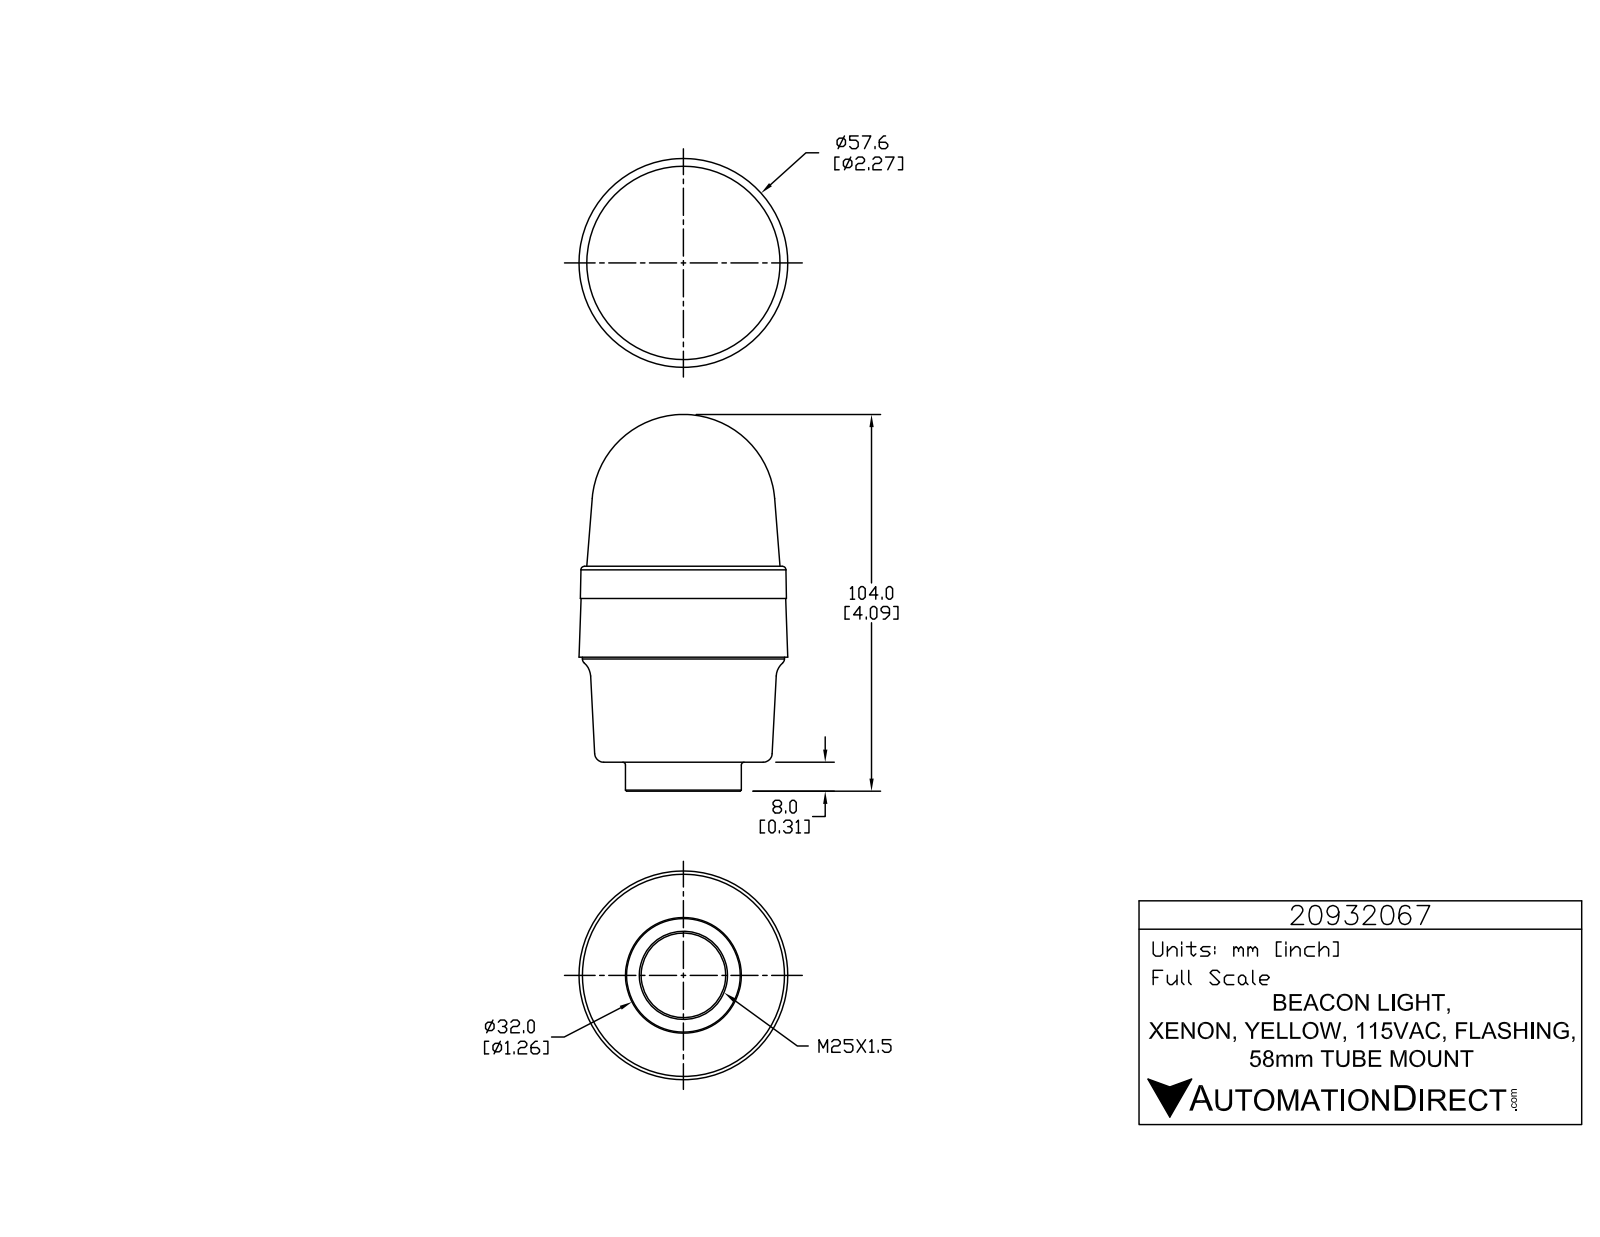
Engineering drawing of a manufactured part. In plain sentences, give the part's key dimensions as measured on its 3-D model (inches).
The part is named "20932067". Its 3-D file was written by "SolidWorks 2015 (AUTOMOTIVE_DESIGN)". It is 1 solid with 791 faces: 525 planar, 168 cylindrical and 98 other. Overall it measures 4.051 by 2.269 by 2.269 inches. Its volume is 11.72 cubic inches and its surface area 29.93 square inches. Round holes: 3 of diameter 0.039, 1 of diameter 0.92. Round bosses or shafts: 3 of diameter 0.226, 3 of diameter 0.056, 1 of diameter 2.197, 1 of diameter 1.26. Partial cylindrical surfaces (rounded edges, fillets, slot ends): 6 of radius 0.008, 6 of radius 0.008, 6 of radius 0.008, 6 of radius 0.131, 3 of radius 0.004, 3 of radius 0.005, 3 of radius 0.008, 3 of radius 0.008. The main face-to-face distances are 0.315, 1.142, 1.457, 0.988, 2.13, 2.445, 0.35, 0.638, 1.78, 2.094.
